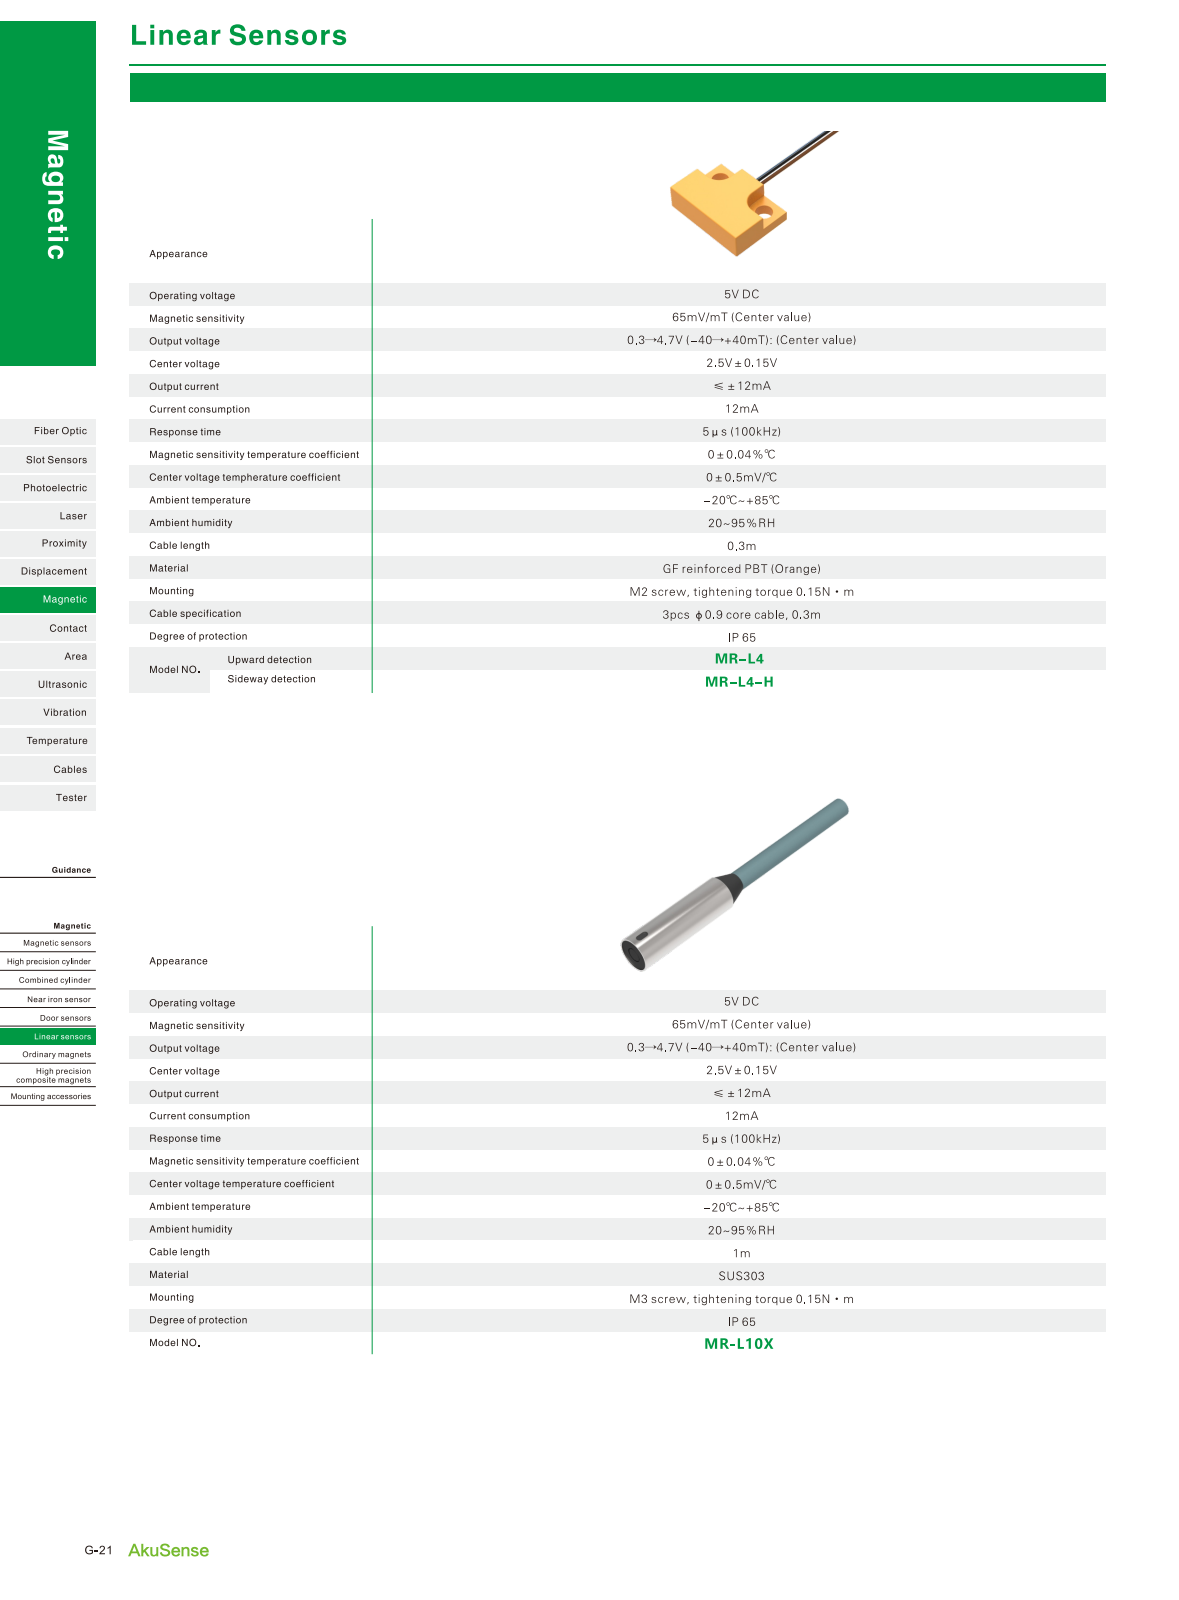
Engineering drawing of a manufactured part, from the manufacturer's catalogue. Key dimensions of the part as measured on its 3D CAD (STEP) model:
Part name (STEP PRODUCT): MR-L10X
STEP written by: SolidWorks 2016 (CONFIG_CONTROL_DESIGN)
Units: millimetres
Bodies: 1 solid, 24 faces (9 planar, 11 cylindrical, 4 other)
Overall size (bounding box): 41.1 × 4.9 × 4.9
Volume: 471 mm³ · Surface area: 507 mm²
Round holes (diameter × count): ⌀2.14 ×1, ⌀4.5 ×1
Round bosses / shafts (diameter × count): ⌀4.9 ×1, ⌀2.8 ×1
Partial cylindrical surfaces — rounded edges, fillets, slot ends (radius × count): R0.44 ×2
Main face-to-face distances: 41, 41.1, 25.1, 15.9, 16, 40.9, 15.8, 0.88
